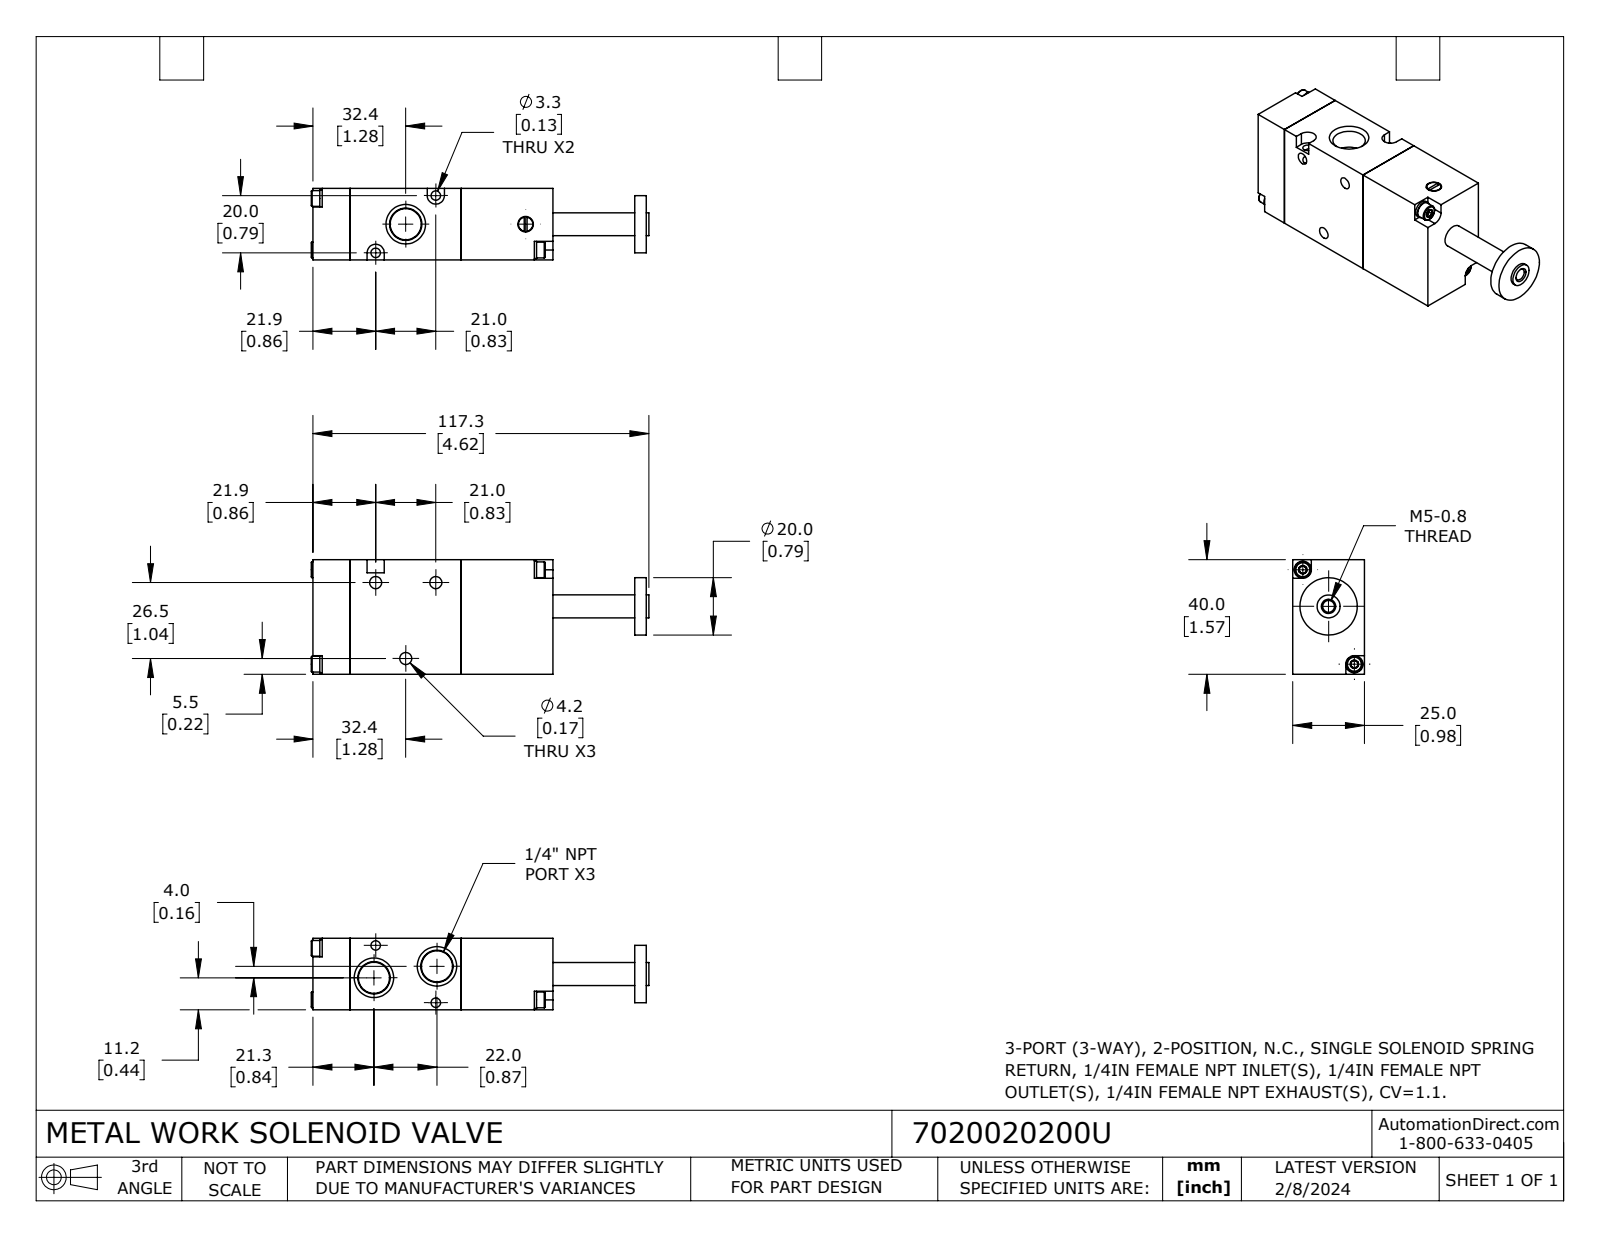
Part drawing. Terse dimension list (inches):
name: 7020020200U
written by: SolidWorks 2023 (CONFIG_CONTROL_DESIGN)
unit: in
bodies: 11 solids, 251 faces (116 planar, 65 cylindrical, 70 other)
size: 4.642 × 1.575 × 0.984
volume: 5.01 in³; area: 34.01 in²
holes: 4× ⌀0.118, 3× ⌀0.165, 2× ⌀0.13, 1× ⌀0.163, 1× ⌀0.213
bosses: 4× ⌀0.236, 4× ⌀0.217, 1× ⌀0.787, 1× ⌀0.315, 1× ⌀0.197
rounds: 2× R0.118
face distances: 0.984, 1.528, 1.575, 0.512, 2.039, 3.299, 2.787, 1.26, 0.311, 1.264
hole spacings: 0.616, 0.709, 0.87, 1.122, 1.299, 1.48, 0.827, 1.142
